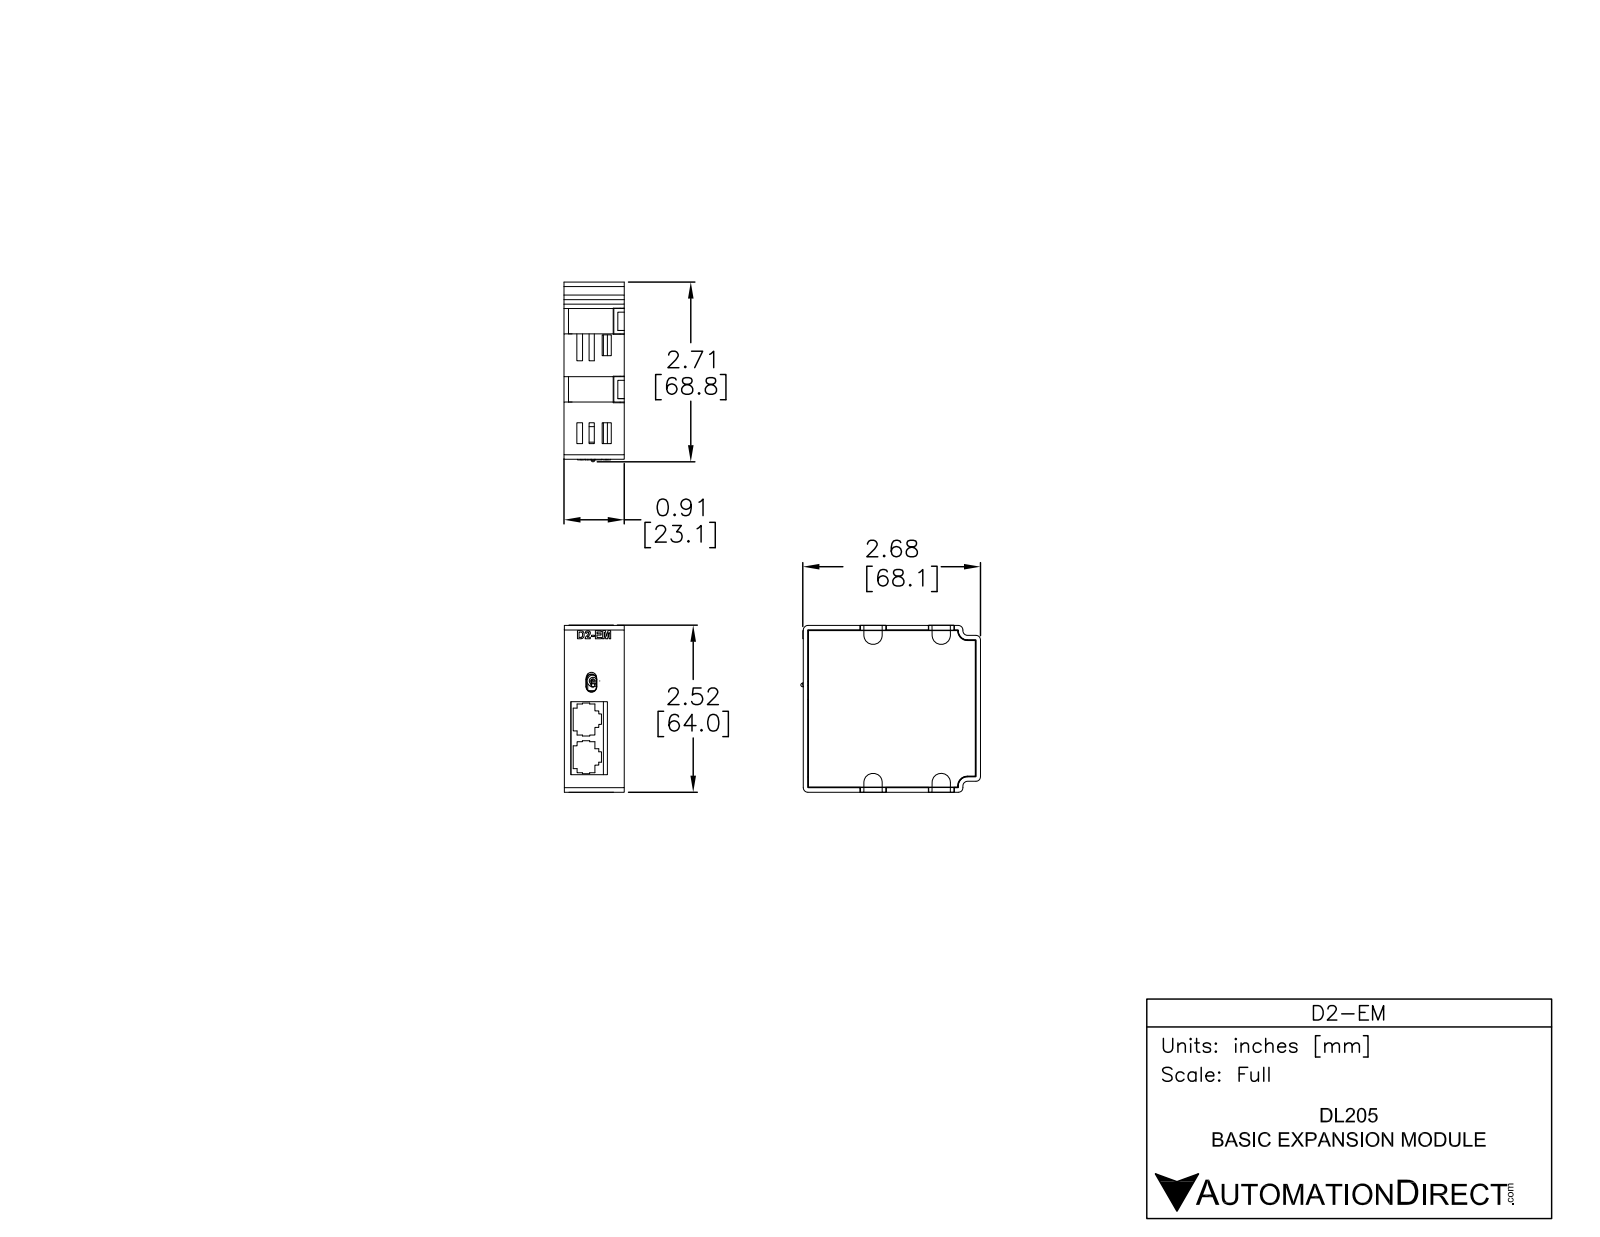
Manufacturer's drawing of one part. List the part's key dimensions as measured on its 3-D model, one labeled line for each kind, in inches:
Part name (STEP PRODUCT): D2-EM_Light_NEW
STEP written by: SolidWorks 2009 (AUTOMOTIVE_DESIGN)
Units: inches
Bodies: 4 solids, 356 faces (295 planar, 40 cylindrical, 21 other)
Overall size (bounding box): 2.715 × 2.524 × 0.906
Volume: 1.972 in³ · Surface area: 57.68 in²
Round holes (diameter × count): ⌀0.112 ×1
Round bosses / shafts (diameter × count): ⌀0.178 ×1, ⌀0.057 ×1
Partial cylindrical surfaces — rounded edges, fillets, slot ends (radius × count): R0.069 ×8, R0.191 ×8, R0.138 ×4, R0.079 ×2, R0.138 ×2, R0.144 ×2
Main face-to-face distances: 0.069, 0.906, 0.837, 0.843, 0.774, 0.063, 0.65, 0.193, 0.256, 0.059
